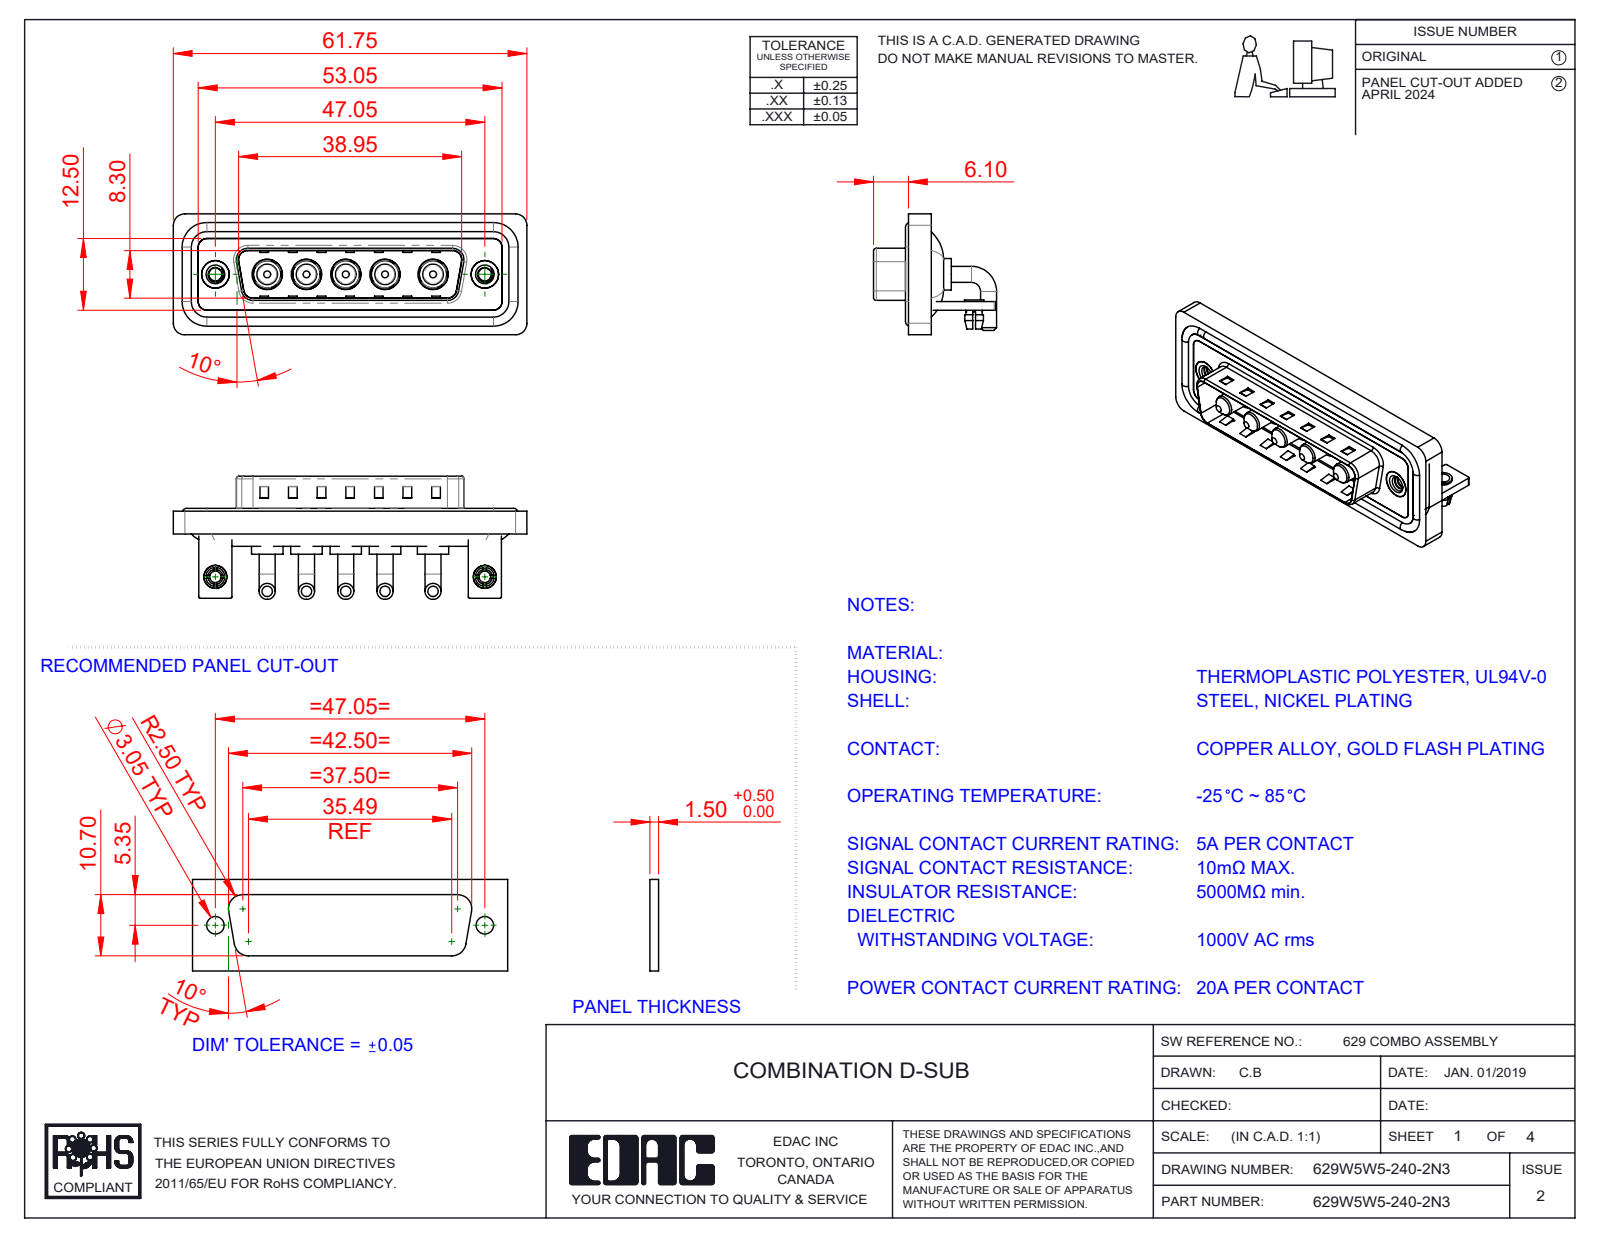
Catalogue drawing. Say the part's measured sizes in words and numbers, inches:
The part is named "629Combo Housing_5W5; 629Combo Stabilizer Bracket; 629W5W5-140-2N3; 629Combo Threaded Rivet_3 (+5 more)". Its 3-D file was written by "SolidWorks 2023 (CONFIG_CONTROL_DESIGN)". It is 21 solids with 830 faces: 327 planar, 343 cylindrical and 160 other. Overall it measures 2.431 by 0.846 by 0.831 inches. Its volume is 0.495 cubic inches and its surface area 20.26 square inches. Round holes: 5 of diameter 0.191, 5 of diameter 0.209, 2 of diameter 0.079, 2 of diameter 0.089, 2 of diameter 0.098, 2 of diameter 0.126, 2 of diameter 0.157, 2 of diameter 0.189, 2 of diameter 0.197. Round bosses or shafts: 10 of diameter 0.11, 5 of diameter 0.217, 5 of diameter 0.205, 5 of diameter 0.187, 5 of diameter 0.148, 5 of diameter 0.142, 4 of diameter 0.063, 2 of diameter 0.193. Partial cylindrical surfaces (rounded edges, fillets, slot ends): 19 of radius 0.079, 18 of radius 0.059, 16 of radius 0.01, 9 of radius 0.02, 8 of radius 0.063, 5 of radius 0.083, 4 of radius 0.024, 4 of radius 0.026. The main face-to-face distances are 0.016, 0.059, 0.114, 0.031, 0.083, 0.043, 0.146, 0.177, 0.161, 0.047. The hole center spacings are 0.27, 0.541, 1.852, 0.27, 0.27, 0.33, 0.33, 0.356.
